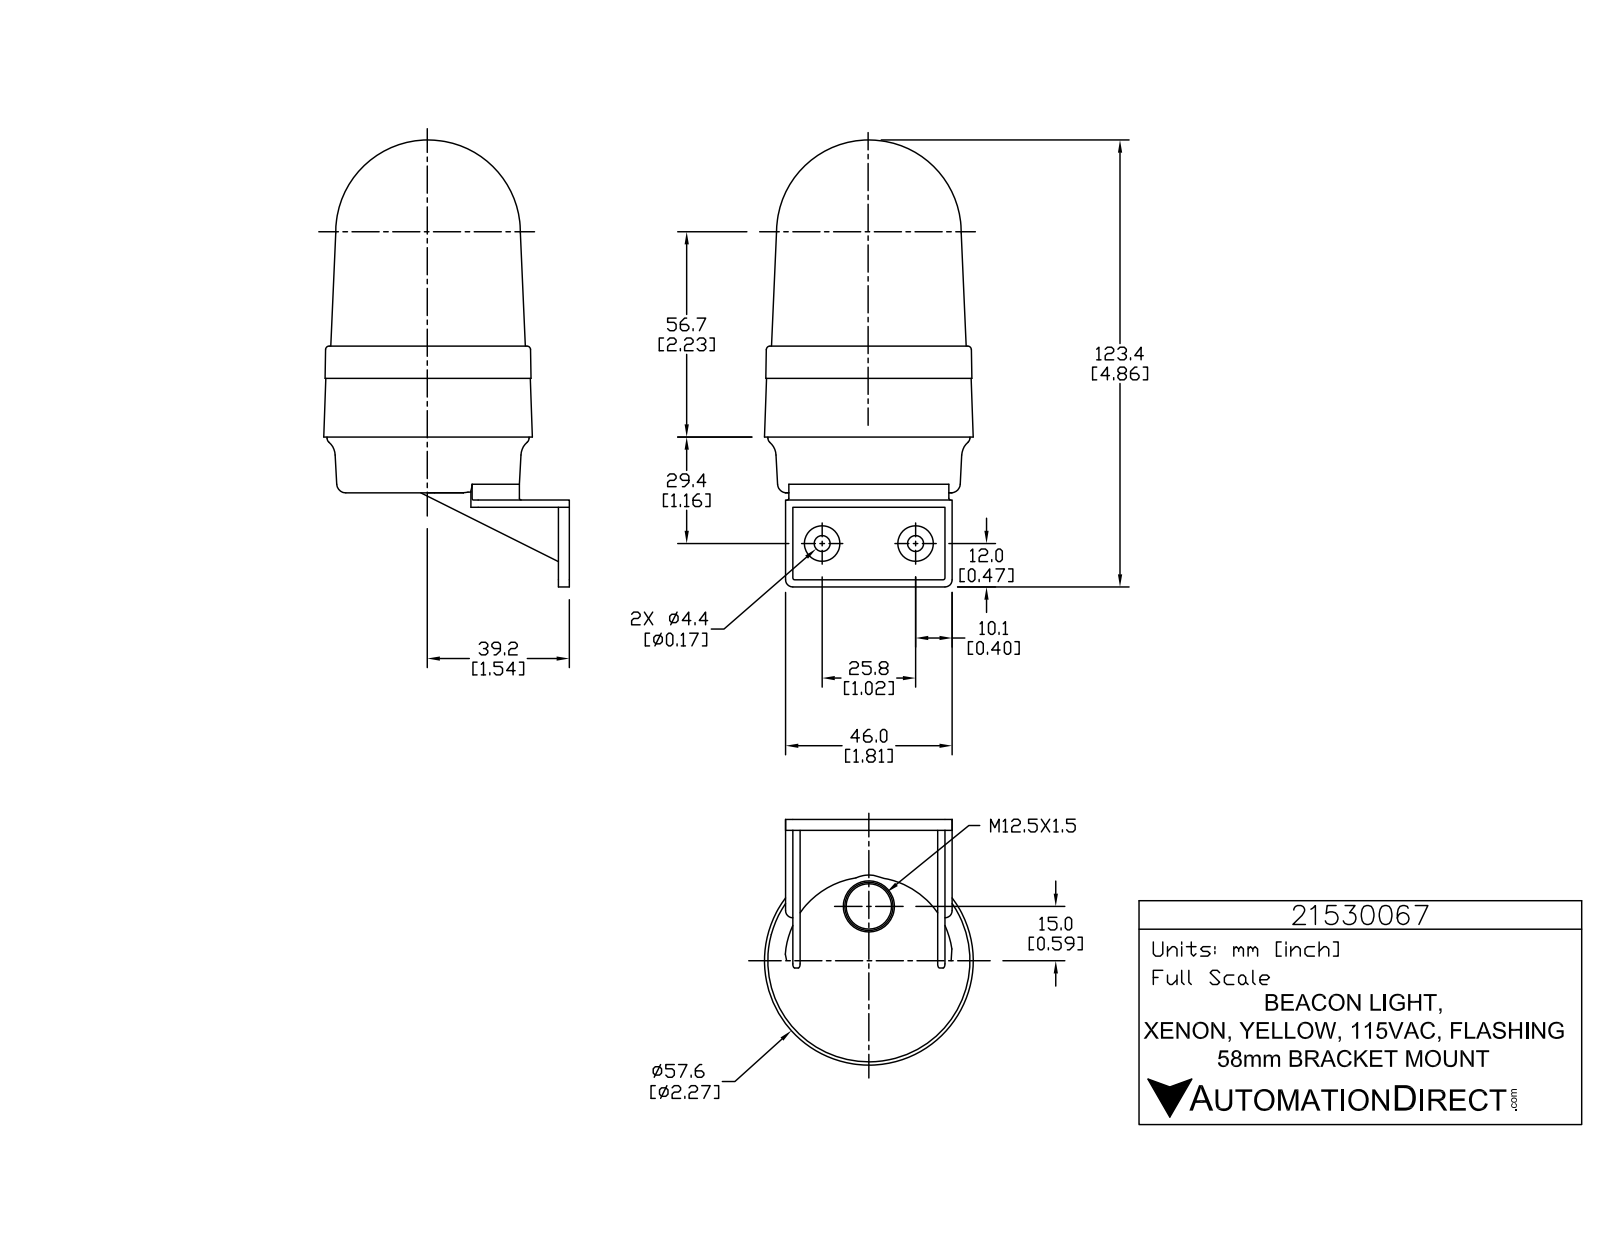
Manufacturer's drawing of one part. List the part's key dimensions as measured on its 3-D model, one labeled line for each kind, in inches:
Part name (STEP PRODUCT): 21530067
STEP written by: SolidWorks 2015 (AUTOMOTIVE_DESIGN)
Units: inches
Bodies: 1 solid, 828 faces (551 planar, 179 cylindrical, 98 other)
Overall size (bounding box): 4.858 × 2.852 × 2.407
Volume: 12.43 in³ · Surface area: 37.49 in²
Round holes (diameter × count): ⌀0.039 ×3, ⌀0.173 ×2
Round bosses / shafts (diameter × count): ⌀0.226 ×3, ⌀0.056 ×3, ⌀0.386 ×2, ⌀2.197 ×1
Partial cylindrical surfaces — rounded edges, fillets, slot ends (radius × count): R0.008 ×6, R0.008 ×6, R0.008 ×6, R0.02 ×6, R0.131 ×6, R0.079 ×4, R0.004 ×3, R0.005 ×3
Main face-to-face distances: 0.079, 0.157, 1.575, 1.654, 0.039, 0.118, 1.496, 0.866, 0.945, 0.764
Hole centre spacings: 1.016
